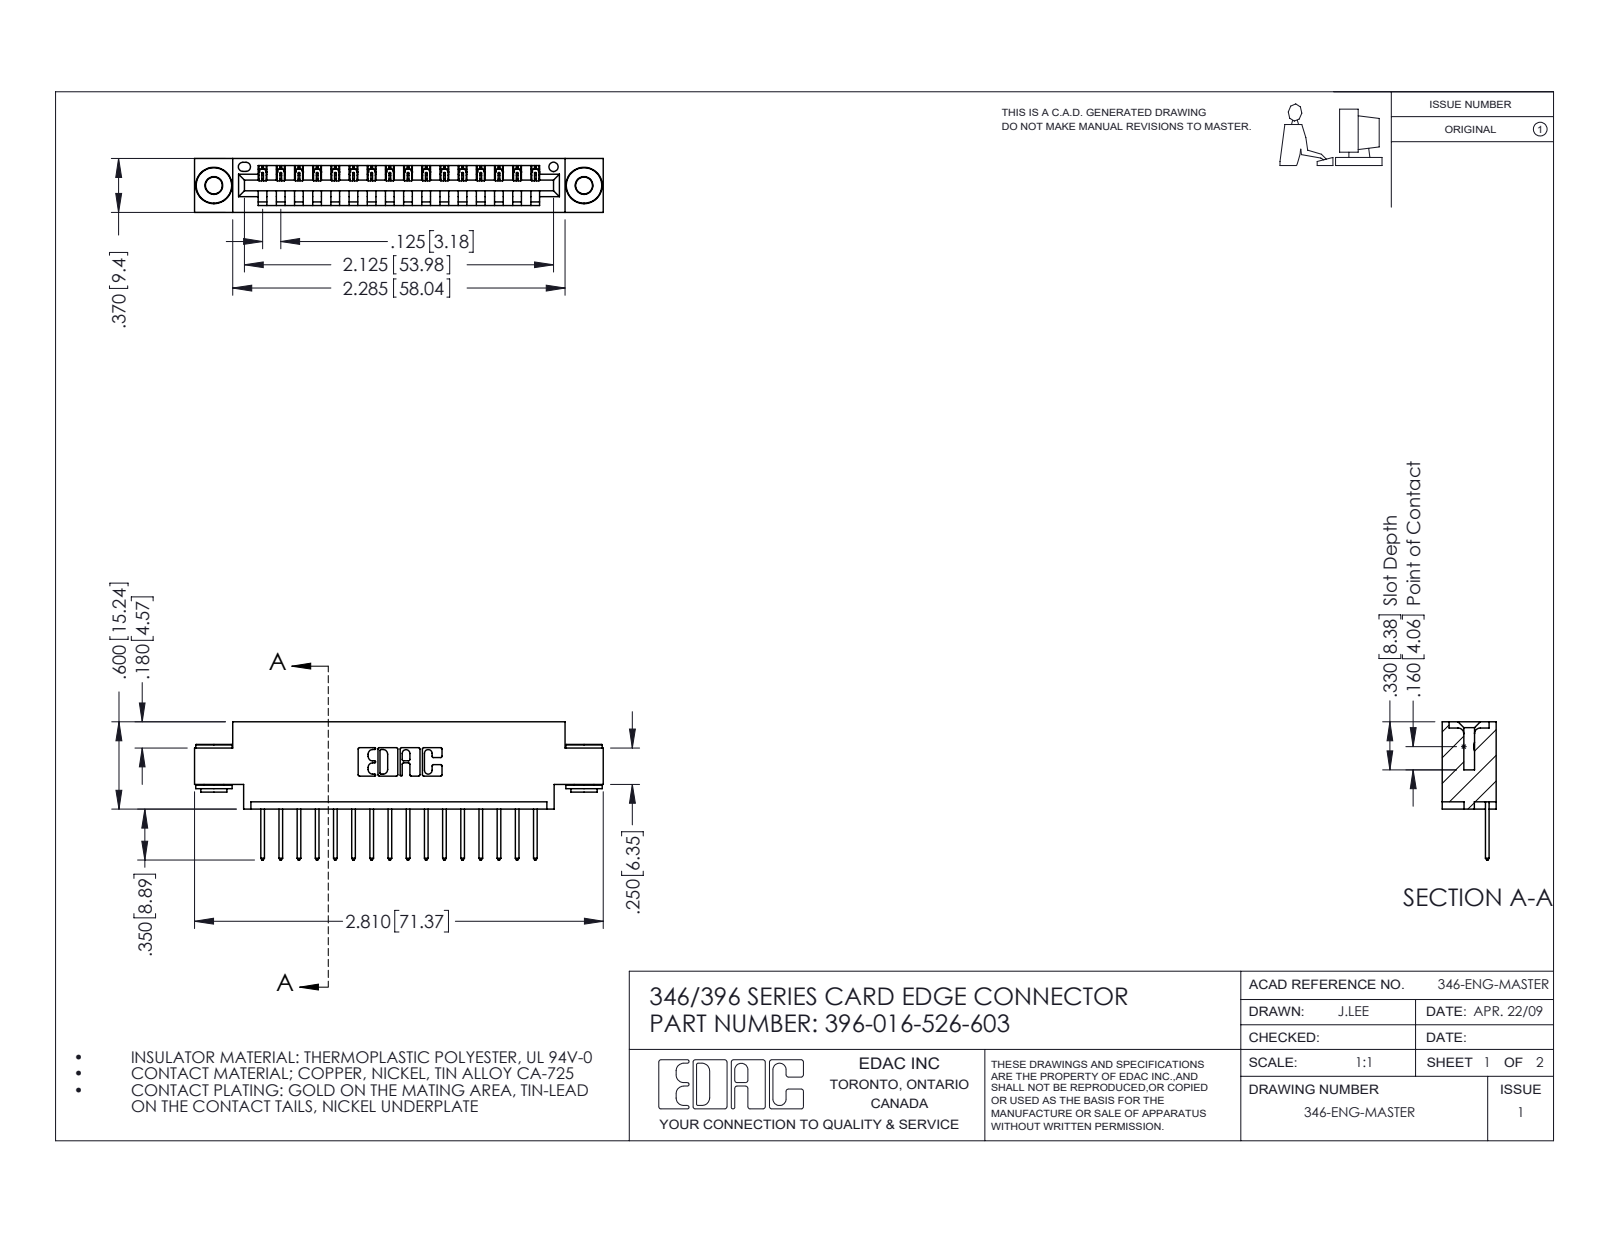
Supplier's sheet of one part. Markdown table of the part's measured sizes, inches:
| quantity | value |
| --- | --- |
| part name | 396-016-526-603; 345-292-001_345-293-126; 345-250-002_345-250-002-102; 346 Part_0.170 Offset - 0.156 Dia-TH |
| STEP written by | SolidWorks 2016 (CONFIG_CONTROL_DESIGN) |
| units | inches |
| bodies | 19 solids, 1092 faces (730 planar, 354 cylindrical, 8 other) |
| overall size | 2.81 × 0.95 × 0.37 |
| volume | 0.397 in³ |
| surface area | 12.73 in² |
| round holes (diameter × count) | 0.116 × 2, 0.156 × 2, 0.064 × 1 |
| round bosses / shafts (diameter × count) | 0.25 × 2, 0.18 × 2, 0.136 × 2 |
| partial cylindrical surfaces (radius × count) | 0.006 × 32, 0.01 × 32, 0.01 × 22, 0.007 × 6, 0.031 × 6, 0.026 × 3, 0.031 × 2, 0.04 × 2 |
| main face-to-face distances | 0.37, 0.048, 0.322, 0.25, 0.025, 0.072, 0.298, 0.148, 0.222, 0.1 |
| hole center spacings | 0.246, 2.338, 2.545 |
